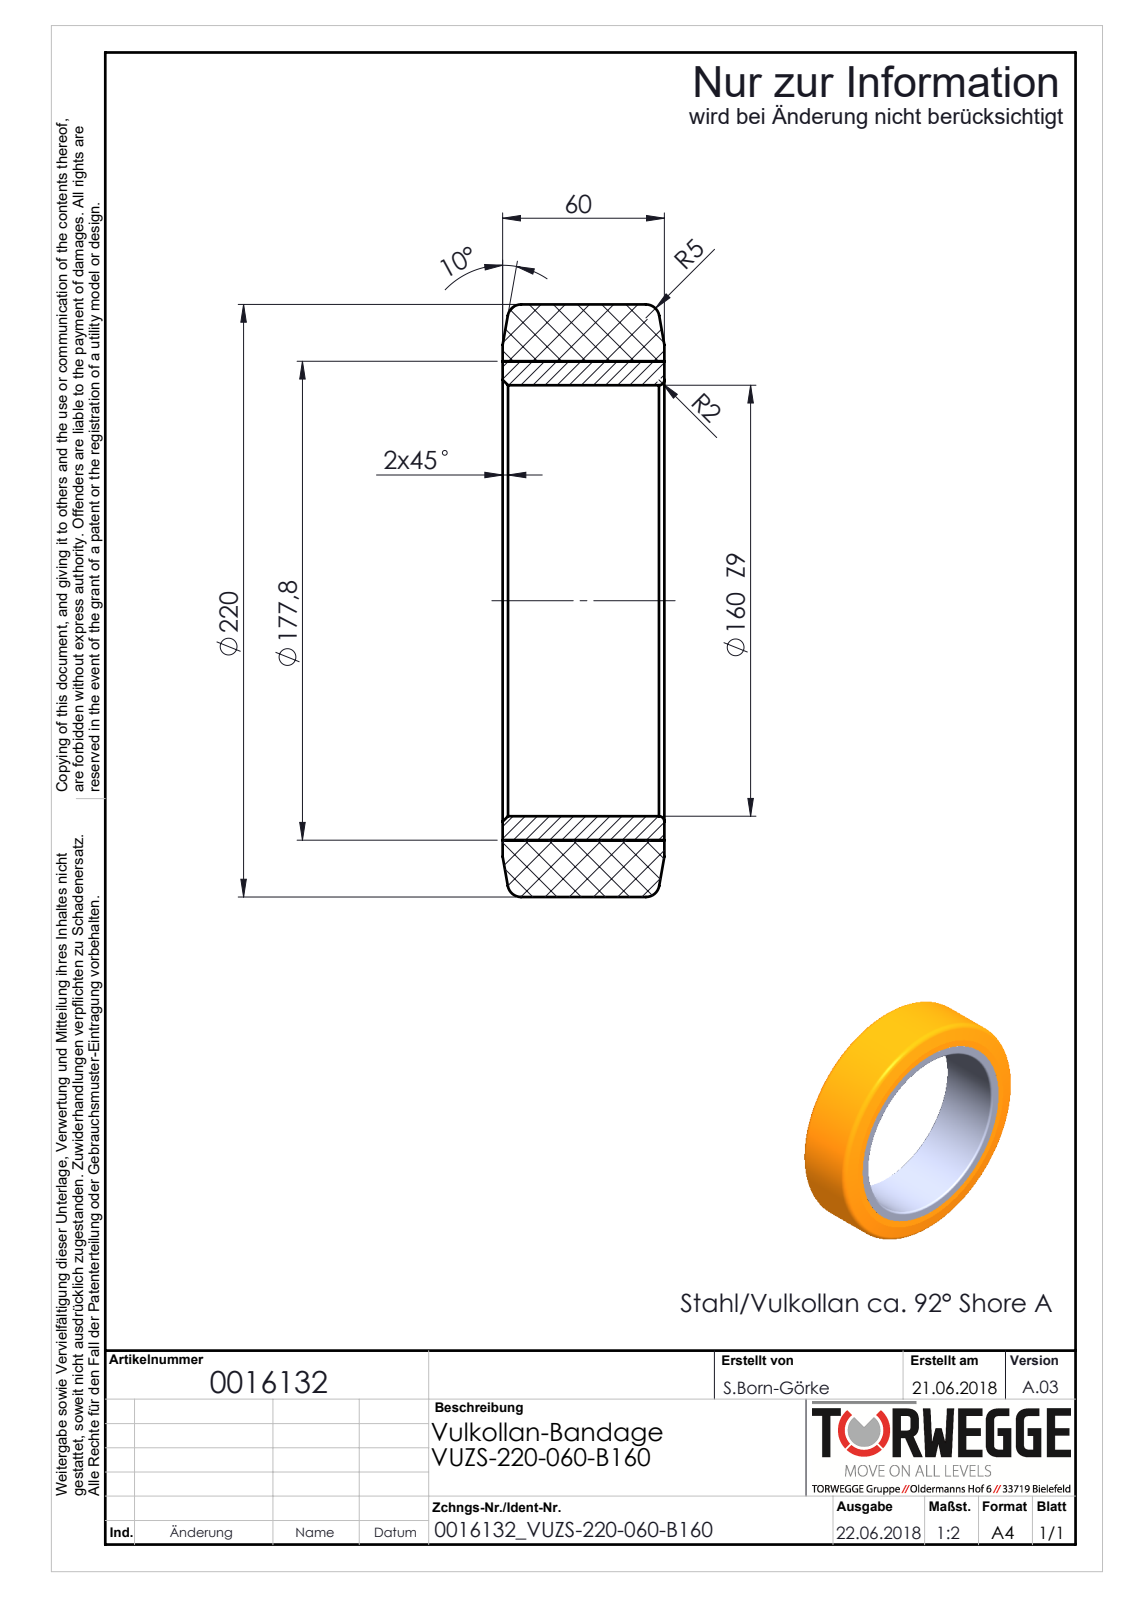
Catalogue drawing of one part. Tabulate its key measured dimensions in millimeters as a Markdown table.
| quantity | value |
| --- | --- |
| part name | 0016132_VUZS-220-060-B160 |
| STEP written by | SolidWorks 2018 (AUTOMOTIVE_DESIGN) |
| units | millimeters |
| bodies | 2 solids, 24 faces (4 planar, 8 cylindrical, 12 other) |
| overall size | 220 × 220 × 60 |
| volume | 1 042 000 mm³ |
| surface area | 168 131 mm² |
| round holes (diameter × count) | 160 × 1, 177.8 × 1 |
| round bosses / shafts (diameter × count) | 220 × 1 |
| main face-to-face distances | 60 |
